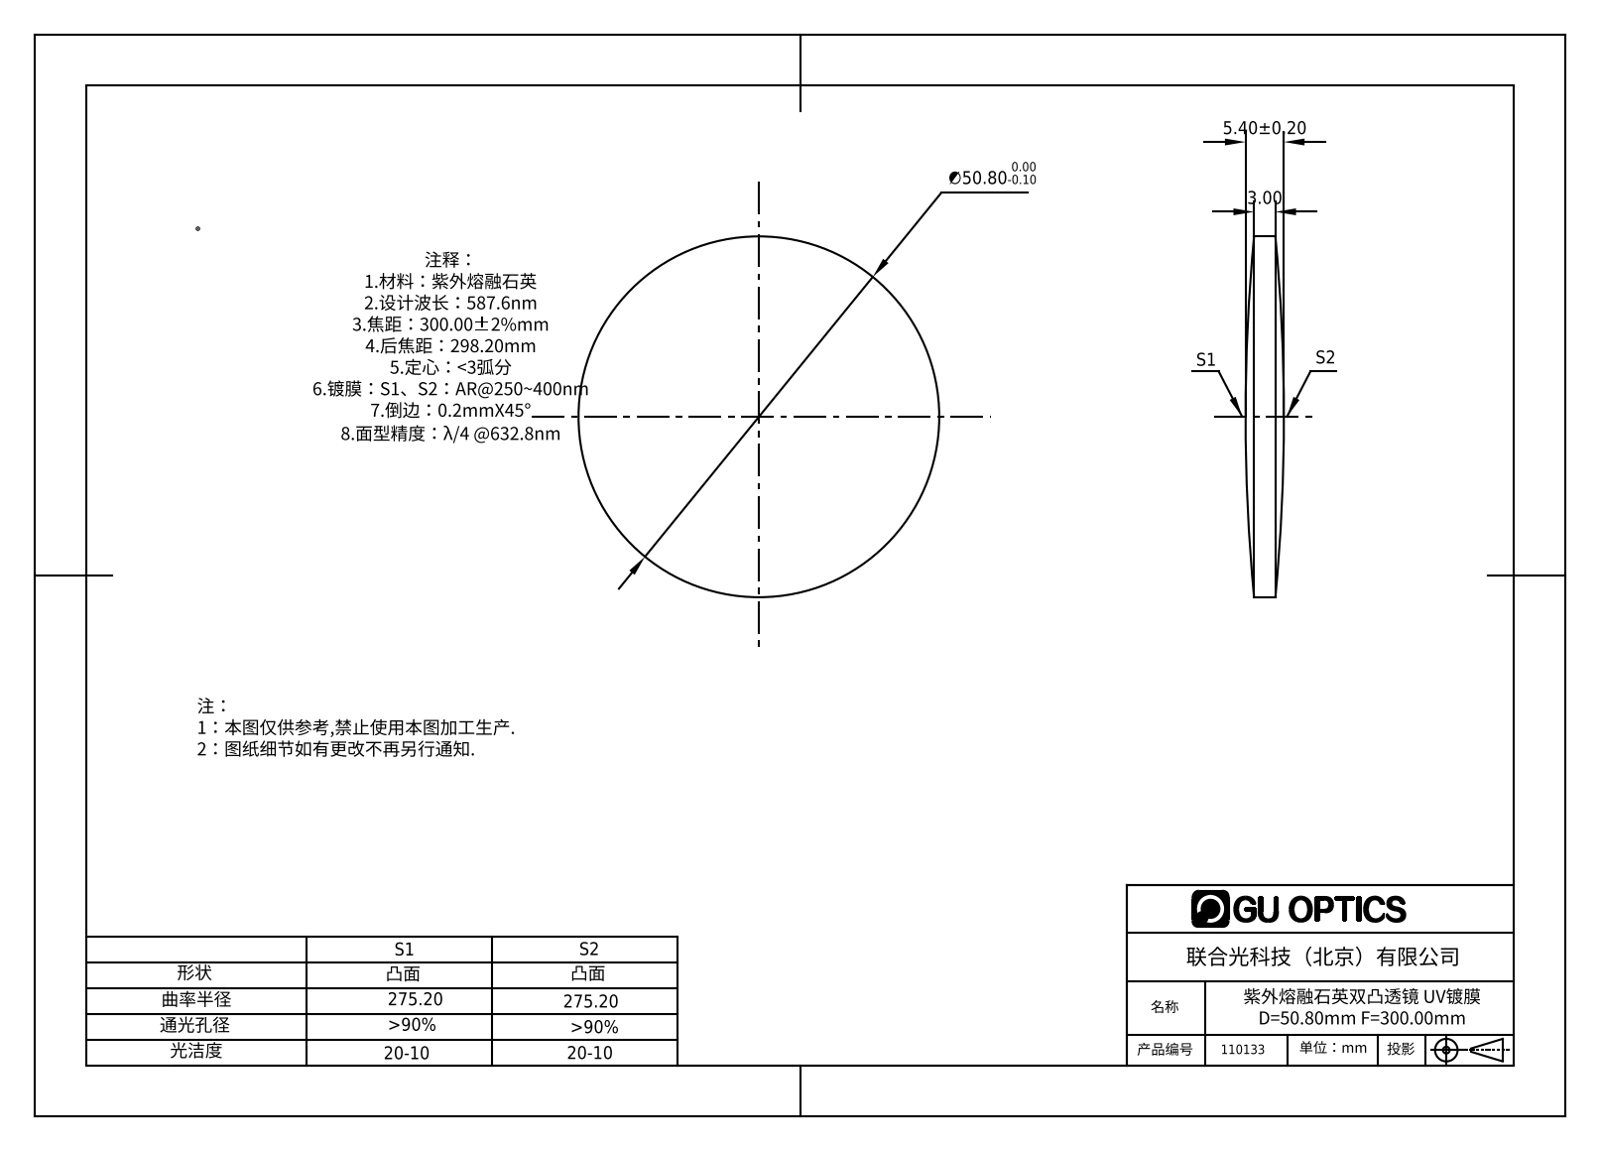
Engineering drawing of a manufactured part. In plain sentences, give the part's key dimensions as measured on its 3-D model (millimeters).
The part is named "110109". Its 3-D file was written by "SolidWorks 2016 (CONFIG_CONTROL_DESIGN)". It is 1 solid with 6 faces: 0 planar, 2 cylindrical and 4 other. Overall it measures 50.8 by 50.8 by 5.4 millimeters. Its volume is 8 514 cubic millimeters and its surface area 4 541 square millimeters. Round bosses or shafts: 1 of diameter 50.8.
